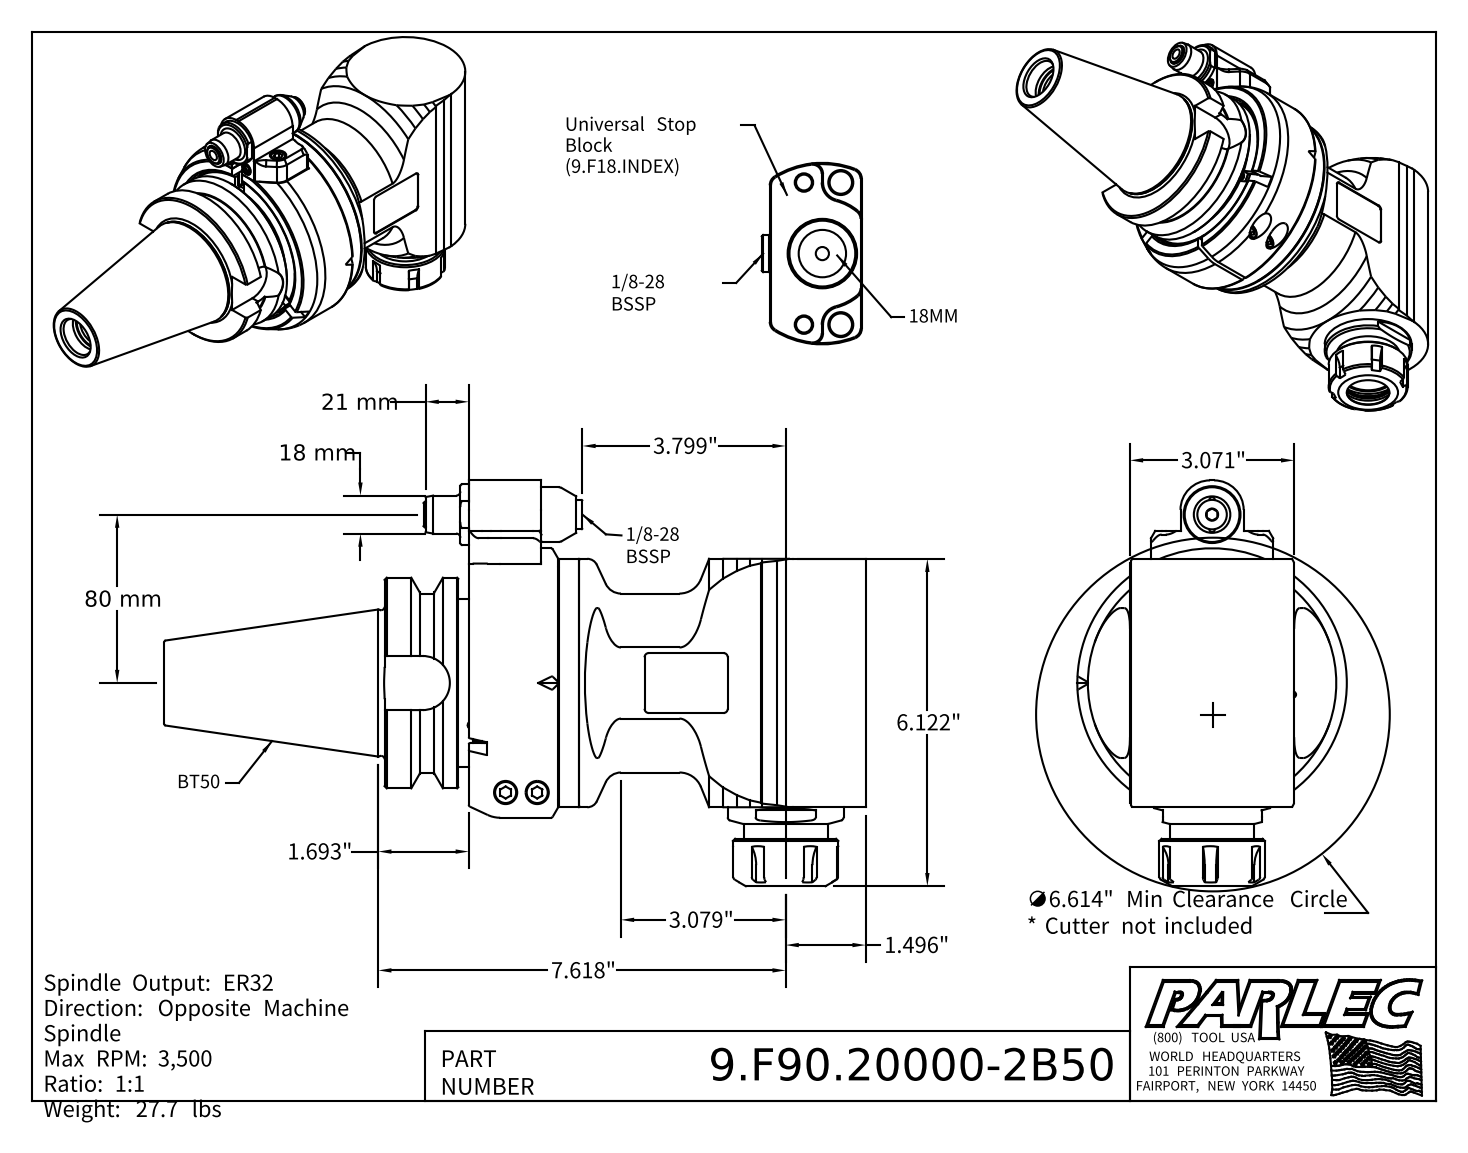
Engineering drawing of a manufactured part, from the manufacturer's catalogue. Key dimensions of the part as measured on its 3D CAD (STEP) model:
Part name (STEP PRODUCT): 9.F90.20000-2B50; 9_GA2_358_2 (Type 2, BT50, 80mm); 9_F90_20000
STEP written by: Autodesk Inventor 2022 (AUTOMOTIVE_DESIGN)
Units: inches
Bodies: 5 solids, 517 faces (240 planar, 118 cylindrical, 159 other)
Overall size (bounding box): 13.122 × 7.589 × 5.039
Volume: 133.3 in³ · Surface area: 348.3 in²
Round holes (diameter × count): ⌀0.197 ×4, ⌀0.492 ×3, ⌀0.102 ×2, ⌀0.165 ×2, ⌀0.209 ×2, ⌀0.315 ×2, ⌀0.409 ×2, ⌀0.433 ×2, ⌀1.063 ×2, ⌀0.098 ×1, ⌀0.118 ×1, ⌀0.256 ×1
Round bosses / shafts (diameter × count): ⌀0.394 ×4, ⌀0.236 ×4, ⌀0.709 ×2, ⌀0.472 ×2, ⌀0.098 ×2, ⌀5.039 ×1, ⌀4.646 ×1, ⌀4.63 ×1
Partial cylindrical surfaces — rounded edges, fillets, slot ends (radius × count): R0.079 ×12, R0.591 ×6, R0.157 ×4, R0.02 ×2, R0.039 ×2, R0.315 ×2, R0.551 ×2, R0.433 ×1
Main face-to-face distances: 0.02, 1.378, 0.039, 1.87, 1.398, 0.079, 0.276, 0.197, 0.256, 1.594
Hole centre spacings: 0.276, 0.512, 0.748, 1.006, 2.491, 0.551, 0.591, 0.63
